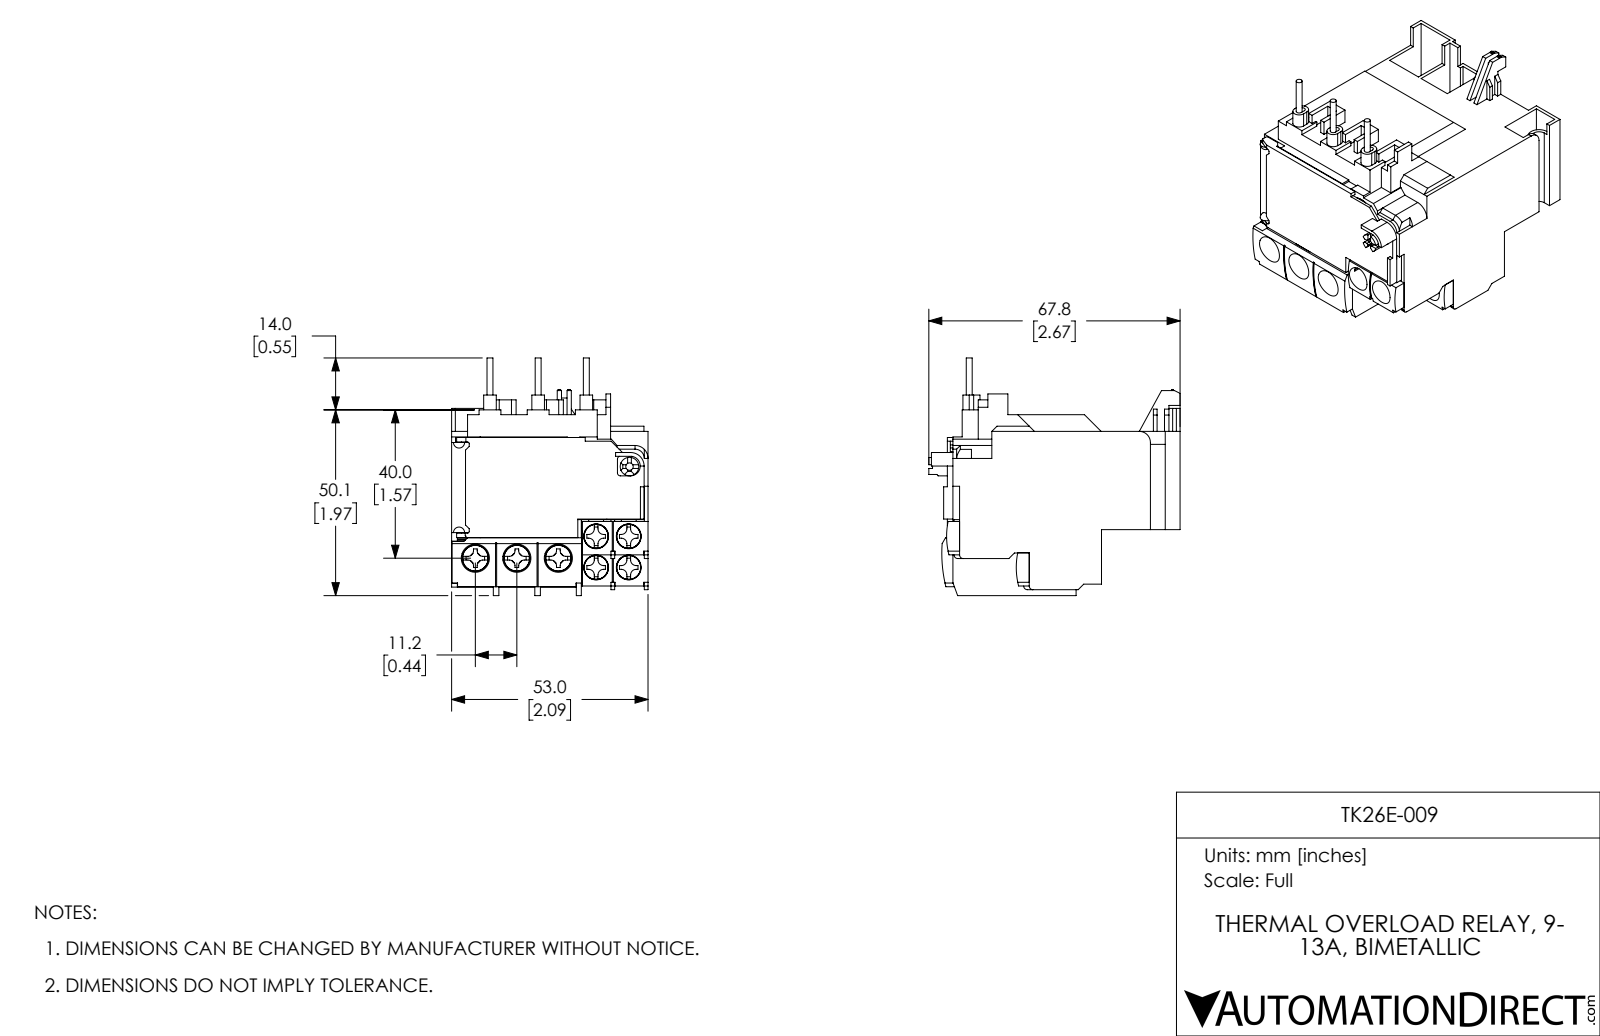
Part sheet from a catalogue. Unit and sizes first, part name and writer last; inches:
Units: inches
Overall size (bounding box): 2.669 × 2.524 × 2.087
Round holes (diameter × count): ⌀0.138 ×4, ⌀0.142 ×4, ⌀0.264 ×4, ⌀0.157 ×3, ⌀0.161 ×3, ⌀0.299 ×3, ⌀0.039 ×1, ⌀0.079 ×1, ⌀0.197 ×1, ⌀0.433 ×1
Round bosses / shafts (diameter × count): ⌀0.26 ×4, ⌀0.063 ×3, ⌀0.236 ×1
Partial cylindrical surfaces — rounded edges, fillets, slot ends (radius × count): R0.059 ×28, R0.039 ×8, R0.02 ×6, R0.067 ×6, R0.031 ×5, R0.047 ×4, R0.171 ×4, R0.189 ×3
Main face-to-face distances: 0.039, 0.354, 0.059, 0.472, 2.087, 0.079, 0.394, 0.433, 0.343, 0.028
Hole centre spacings: 0.331, 0.346, 0.441, 0.479, 0.376, 0.413, 0.464, 0.74
Volume: 6.099 in³ · Surface area: 60.15 in²
Bodies: 38 solids, 1480 faces (1225 planar, 220 cylindrical, 35 other)
Part name (STEP PRODUCT): TK26E-009
STEP written by: SolidWorks 2017 (AUTOMOTIVE_DESIGN)
